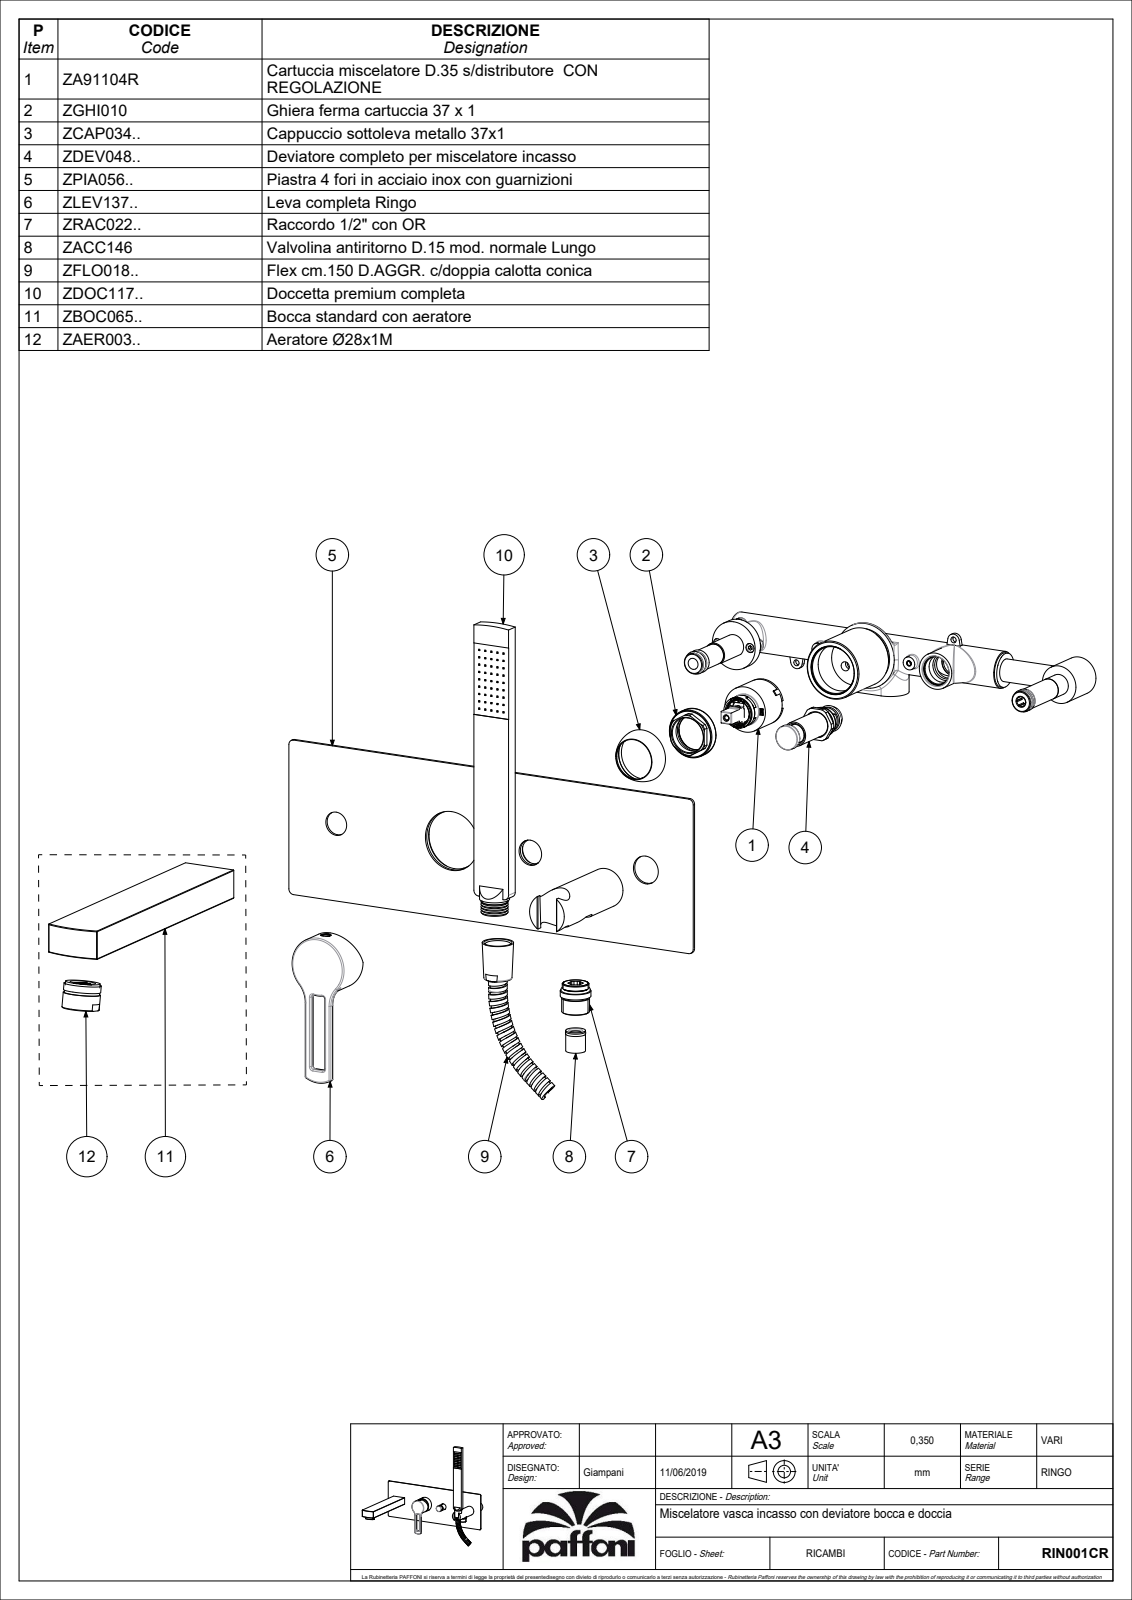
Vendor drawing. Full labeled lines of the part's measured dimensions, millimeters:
Part name (STEP PRODUCT): RIN001CR
STEP written by: CREO PARAMETRIC BY PTC INC, 2020044 (CONFIG_CONTROL_DESIGN)
Units: millimetres
Bodies: 8 solids, 3082 faces (2377 planar, 362 cylindrical, 343 other)
Overall size (bounding box): 356.89 × 329.3 × 210.25
Volume: 408 428 mm³ · Surface area: 219 681 mm²
Round holes (diameter × count): ⌀4 ×2, ⌀8.5 ×2, ⌀16 ×2, ⌀17.3 ×2, ⌀19 ×2, ⌀19.5 ×2, ⌀3 ×1, ⌀3.3 ×1, ⌀4.5 ×1, ⌀5 ×1, ⌀7.5 ×1, ⌀7.8 ×1
Round bosses / shafts (diameter × count): ⌀2 ×11, ⌀22 ×2, ⌀44.8 ×1, ⌀35 ×1, ⌀30 ×1, ⌀28 ×1, ⌀26.5 ×1, ⌀23.5 ×1
Partial cylindrical surfaces — rounded edges, fillets, slot ends (radius × count): R0.5 ×14, R1 ×14, R0.15 ×11, R4 ×6, R0.3 ×4, R2 ×4, R2.25 ×2, R2.5 ×2
Main face-to-face distances: 2, 22, 73.5, 71.5, 10, 83.5, 81.5, 42, 1, 3
Hole centre spacings: 100, 168, 3.5, 11, 40, 68, 99.8, 100.06
